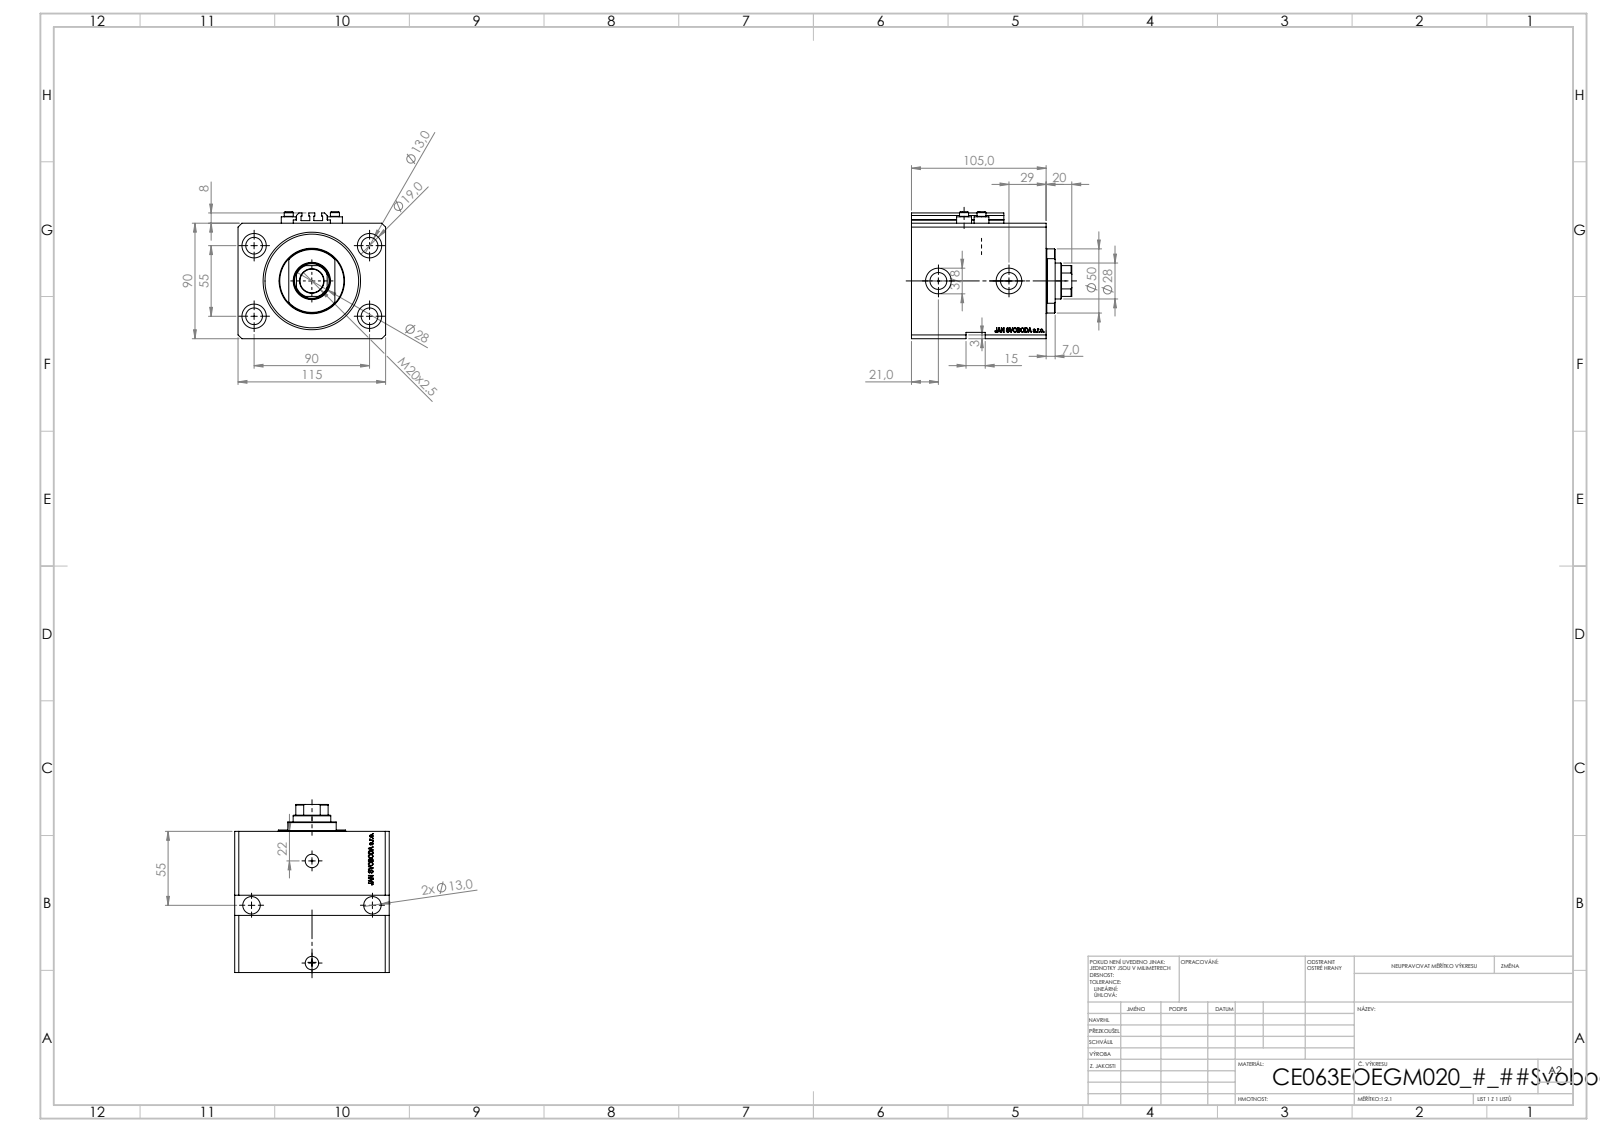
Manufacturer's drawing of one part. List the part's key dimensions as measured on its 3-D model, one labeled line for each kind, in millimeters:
Part name (STEP PRODUCT): V250CE_C_VCP; V250CE_VC_E; V250CE_E_Body; ALLEN BOLT V250CE
STEP written by: SolidWorks 2019 (CONFIG_CONTROL_DESIGN)
Units: millimetres
Bodies: 8 solids, 1107 faces (543 planar, 126 cylindrical, 438 other)
Overall size (bounding box): 125 × 115 × 99
Volume: 954 568 mm³ · Surface area: 153 949 mm²
Round holes (diameter × count): ⌀13 ×6, ⌀1.25 ×4, ⌀4 ×4, ⌀19 ×4, ⌀10 ×2, ⌀13.16 ×2, ⌀20 ×2, ⌀18.5 ×1, ⌀28 ×1, ⌀63 ×1, ⌀76 ×1
Round bosses / shafts (diameter × count): ⌀11.6 ×4, ⌀7 ×4, ⌀50 ×1
Partial cylindrical surfaces — rounded edges, fillets, slot ends (radius × count): R0.2 ×10, R13.5 ×1
Main face-to-face distances: 90, 20, 115, 85, 105, 87.1, 17.9, 67.1, 40, 65
Hole centre spacings: 52.74, 55, 90, 13.6, 27.39, 28.46, 33.62, 36
